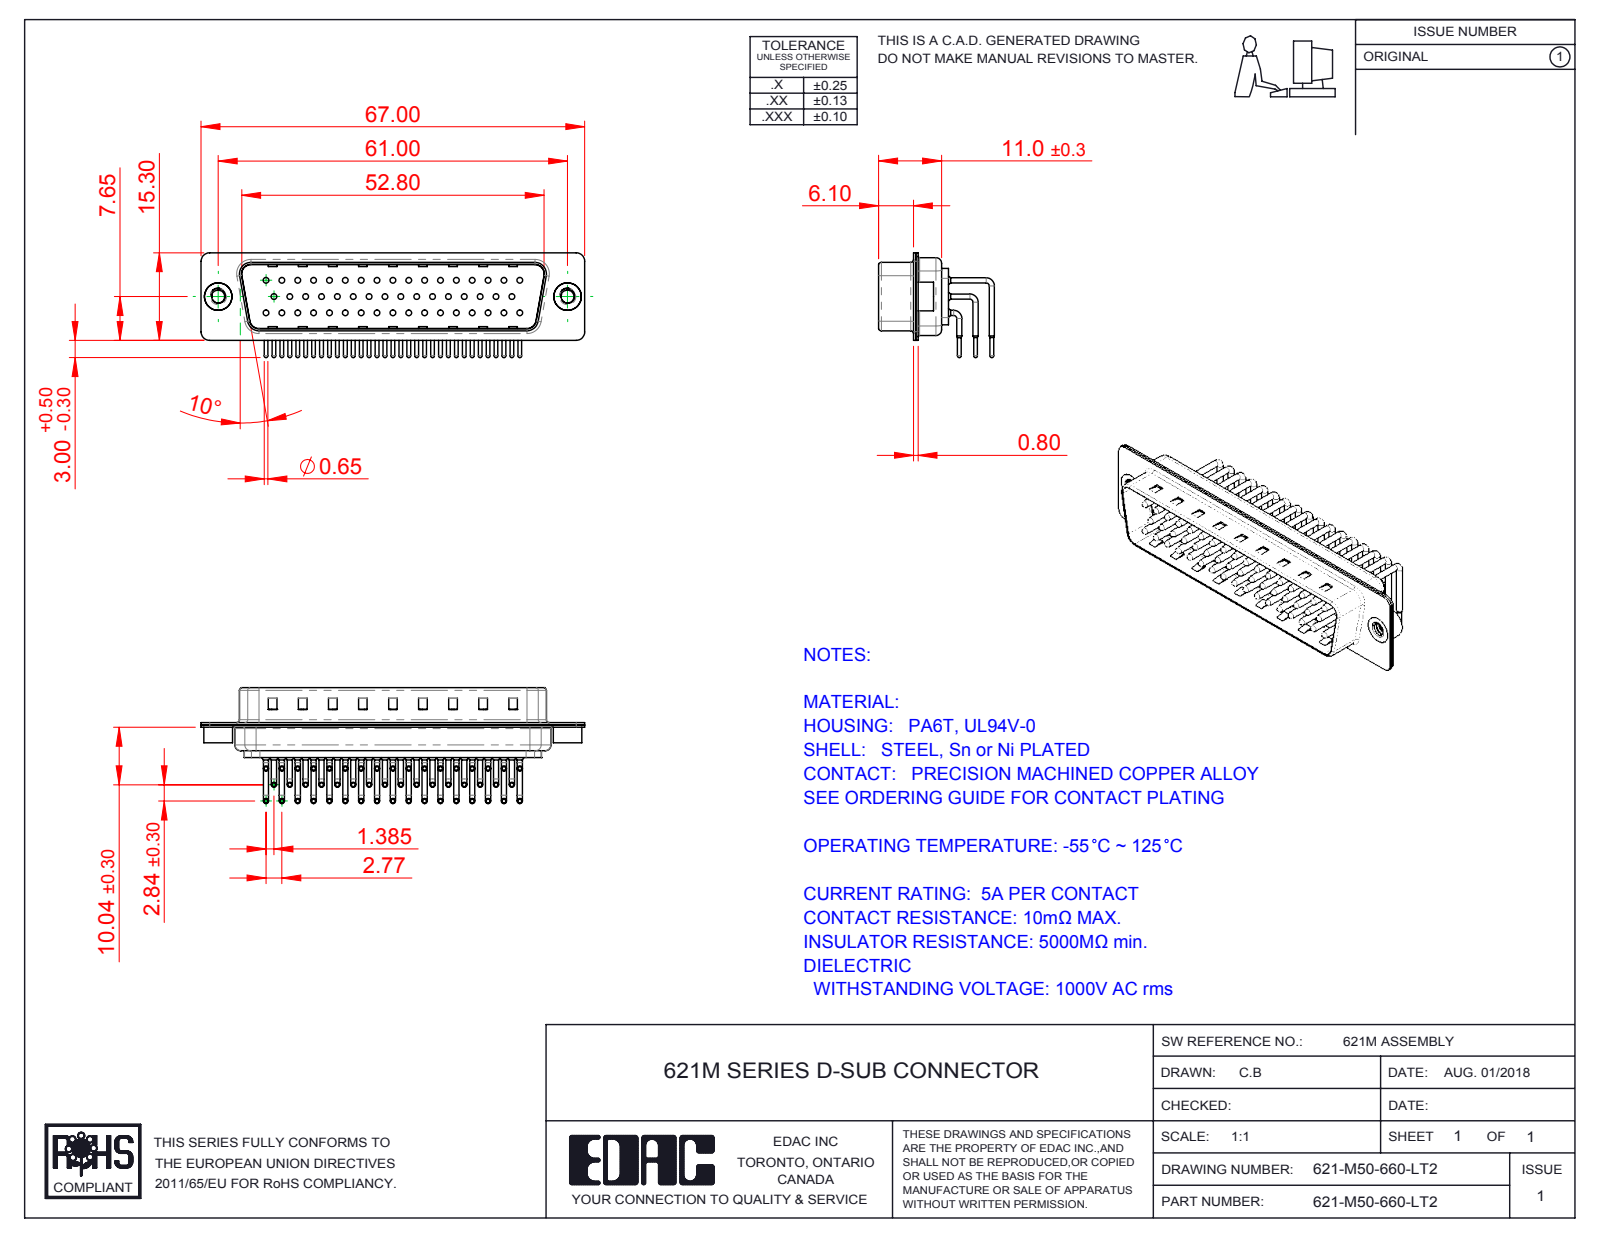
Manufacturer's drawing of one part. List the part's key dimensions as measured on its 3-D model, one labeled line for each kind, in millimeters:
Part name (STEP PRODUCT): 621M Contact Row 1_50 Contacts; 621M Shell Rear_50 Contacts; 621M Contact Row 3; 621M Shell Front_50 Contacts (+4 more)
STEP written by: SolidWorks 2016 (CONFIG_CONTROL_DESIGN)
Units: millimetres
Bodies: 55 solids, 5912 faces (3403 planar, 1941 cylindrical, 568 other)
Overall size (bounding box): 67 × 20.23 × 18.3
Volume: 4 922 mm³ · Surface area: 12 575 mm²
Round holes (diameter × count): ⌀1 ×50, ⌀1.7 ×50, ⌀2 ×50, ⌀2.26 ×2, ⌀4 ×2, ⌀4.8 ×2
Round bosses / shafts (diameter × count): ⌀0.9 ×100, ⌀1.5 ×50, ⌀0.65 ×50, ⌀5 ×2, ⌀4.9 ×2
Partial cylindrical surfaces — rounded edges, fillets, slot ends (radius × count): R1.01 ×50, R1.5 ×16, R2 ×12, R0.5 ×8, R1.6 ×8, R0.25 ×4, R0.6 ×4, R0.65 ×4
Main face-to-face distances: 0.4, 11.55, 5.7, 6.1, 12.38, 0.83, 0.82, 12.37, 13.2, 4.2
Hole centre spacings: 2.77, 3.16, 5.54, 8.31, 11.08, 13.85, 16.62, 19.39
